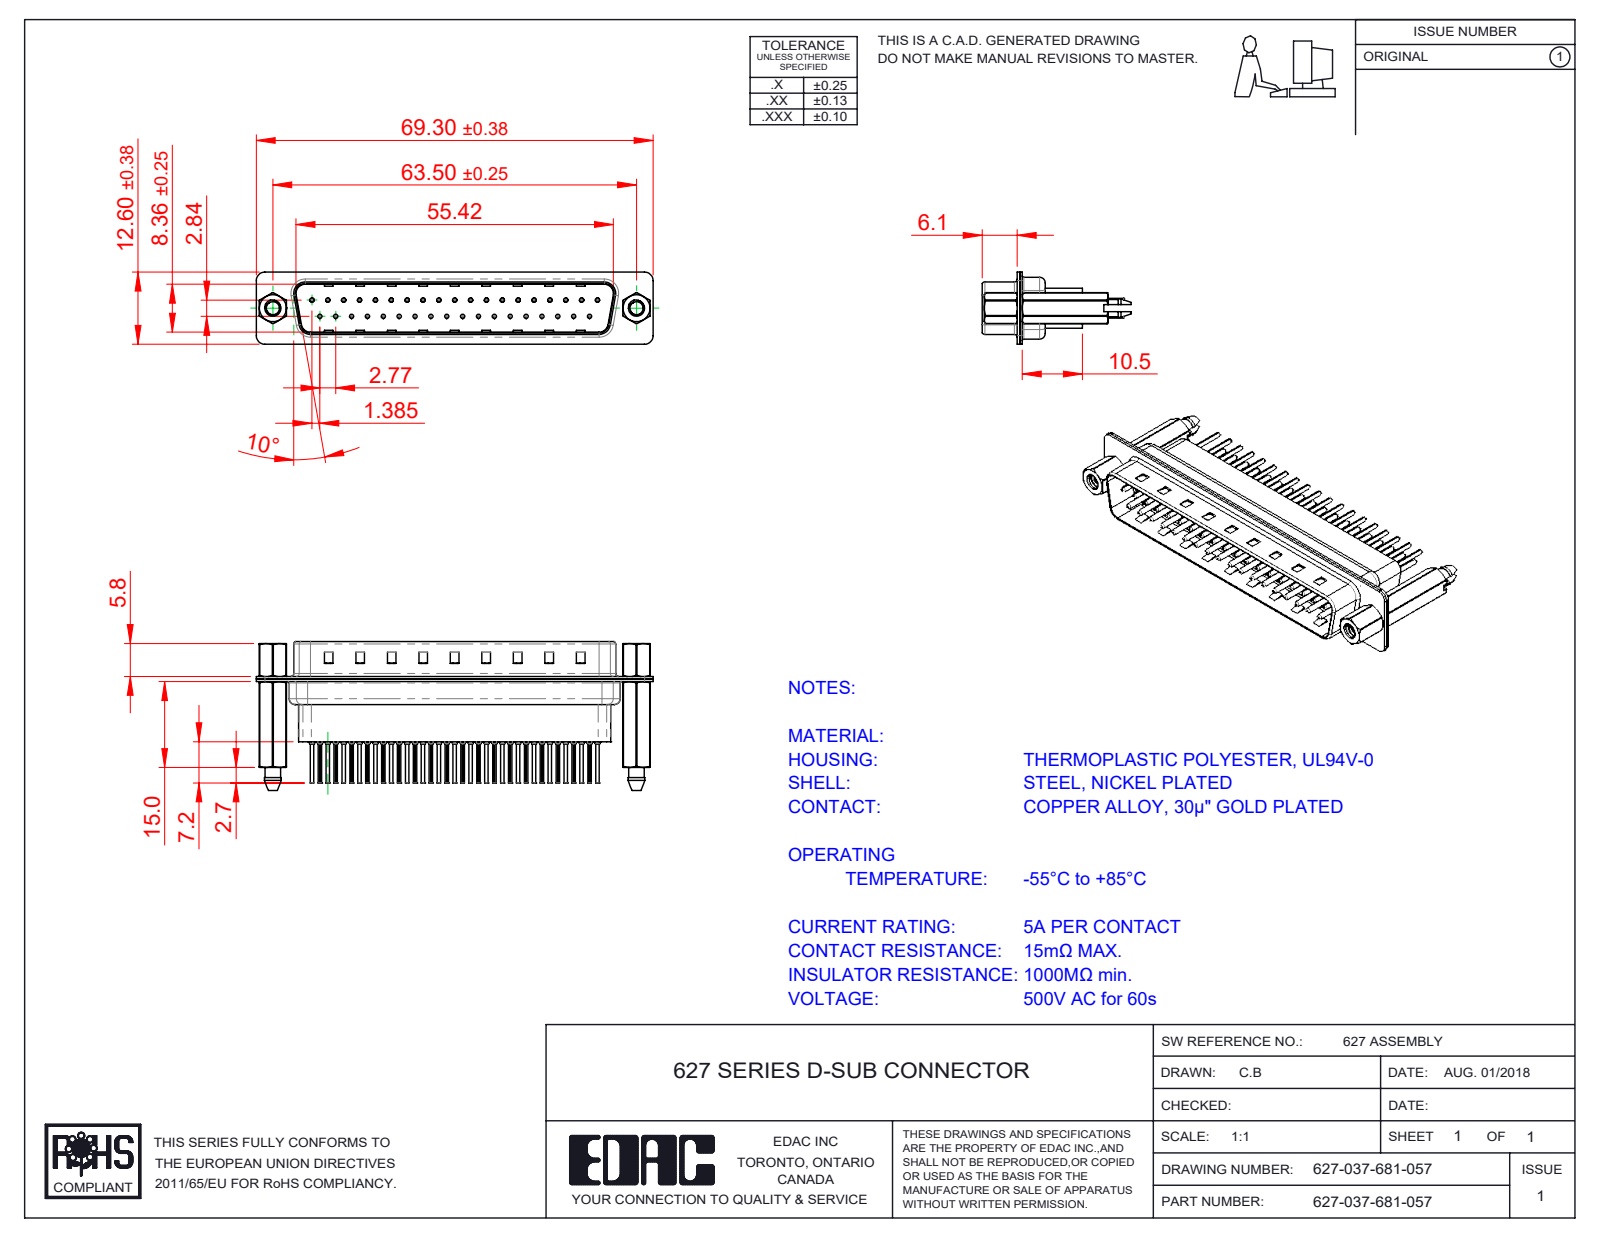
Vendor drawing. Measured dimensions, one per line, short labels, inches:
name: 627 4-40 Hex Standoff; 627 Housing_37 HP; 627 Shell Front_37 Contacts; 627 4-40 Threaded Boardlock_HP81 (+4 more)
written by: SolidWorks 2020 (CONFIG_CONTROL_DESIGN)
unit: in
bodies: 44 solids, 4272 faces (1145 planar, 1648 cylindrical, 1479 other)
size: 2.728 × 1.02 × 0.496
volume: 0.362 in³; area: 23.6 in²
holes: 37× ⌀0.008, 37× ⌀0.014, 37× ⌀0.043, 37× ⌀0.063, 2× ⌀0.089, 2× ⌀0.09, 2× ⌀0.157, 2× ⌀0.189
bosses: 37× ⌀0.079, 37× ⌀0.059, 37× ⌀0.03, 37× ⌀0.024, 2× ⌀0.193, 2× ⌀0.11
rounds: 74× R0.004, 18× R0.059, 12× R0.079, 10× R0.063, 8× R0.02, 4× R0.01, 4× R0.024, 4× R0.026
face distances: 0.016, 0.032, 0.377, 0.018, 0.027, 0.302, 0.059, 0.043, 0.318, 0.345
hole spacings: 0.124, 0.109, 0.218, 0.327, 0.198, 0.398, 0.436, 0.503
